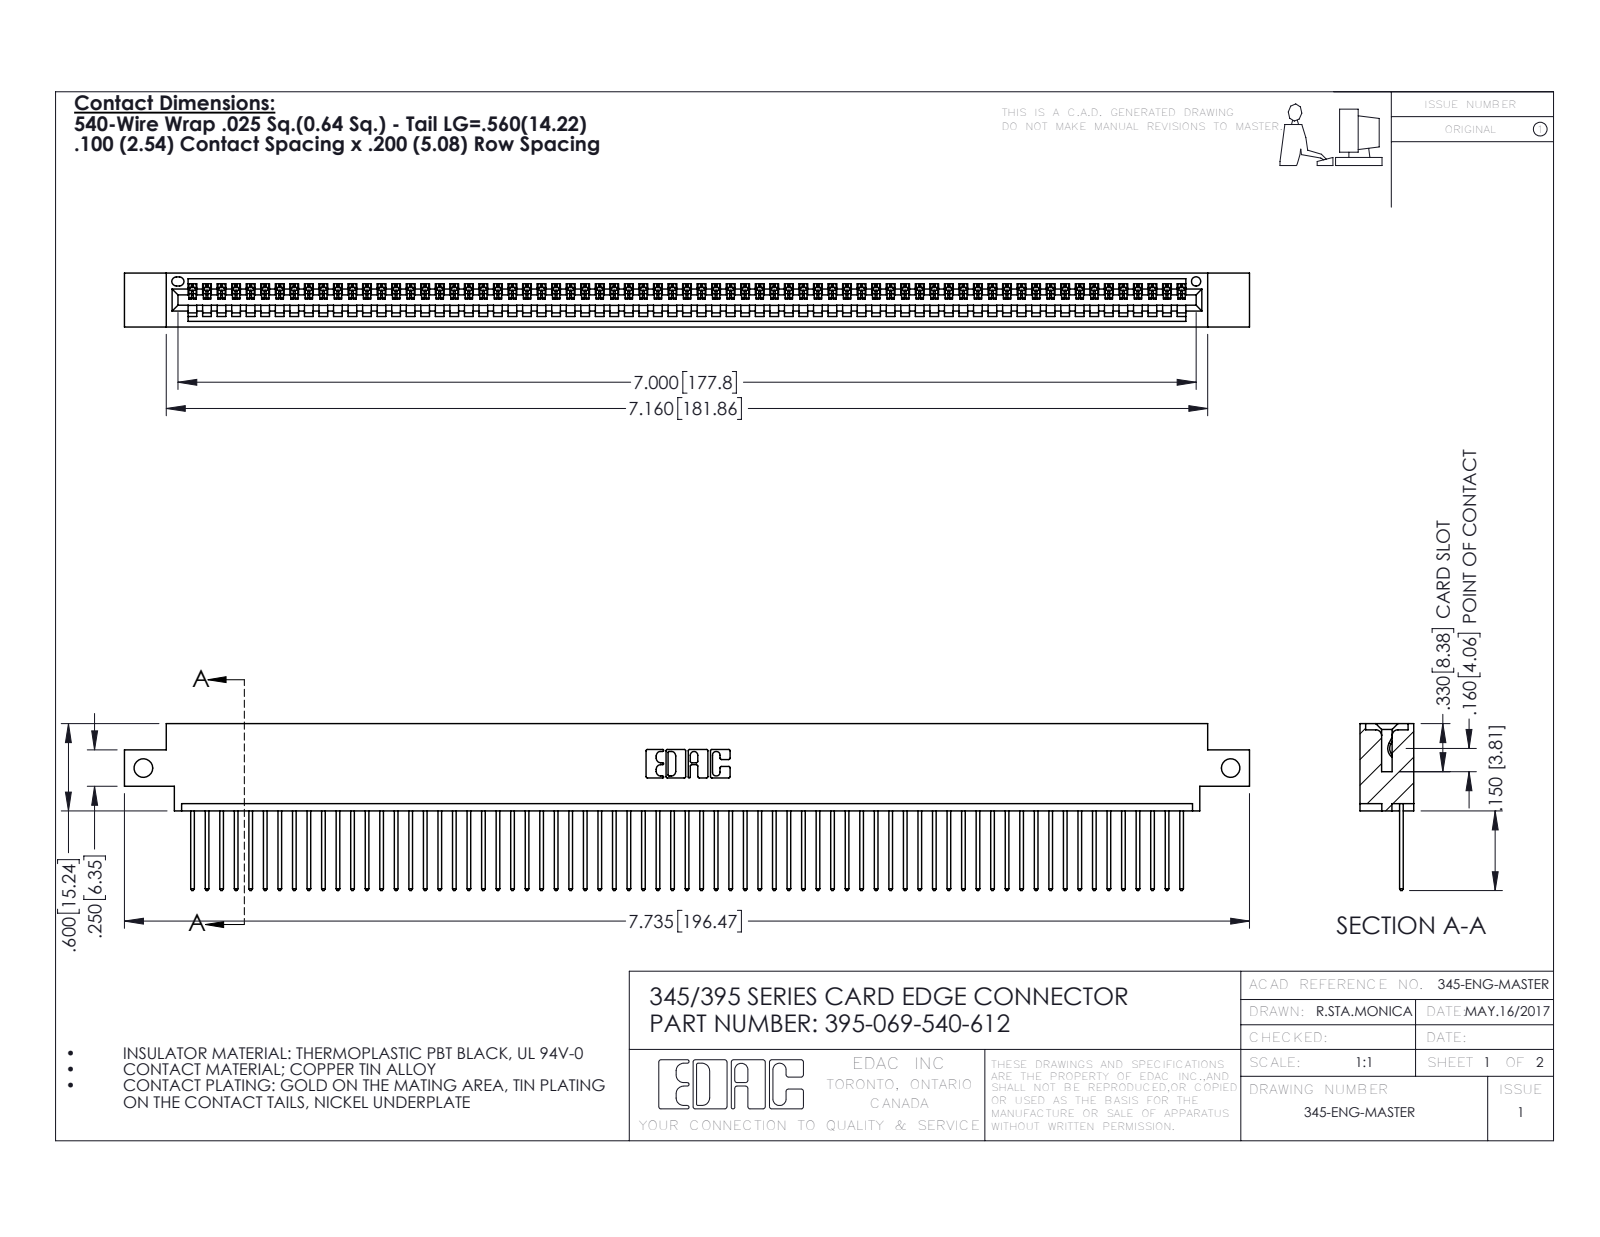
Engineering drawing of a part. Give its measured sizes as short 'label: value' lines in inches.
name: 395-069-540-612; 345 Part_0.170 Offset - Side Mount; 345-292-001_345-293-140
written by: SolidWorks 2016 (CONFIG_CONTROL_DESIGN)
unit: in
bodies: 70 solids, 4132 faces (2844 planar, 1288 cylindrical, 0 other)
size: 7.735 × 1.147 × 0.37
volume: 1.146 in³; area: 40.26 in²
holes: 2× ⌀0.128, 1× ⌀0.064
rounds: 138× R0.006, 138× R0.01, 22× R0.01, 6× R0.007, 6× R0.031, 3× R0.026, 2× R0.031, 2× R0.04
face distances: 0.072, 0.298, 0.37, 0.098, 0.272, 0.025, 0.2, 0.225, 0.175, 0.149
hole spacings: 7.475
